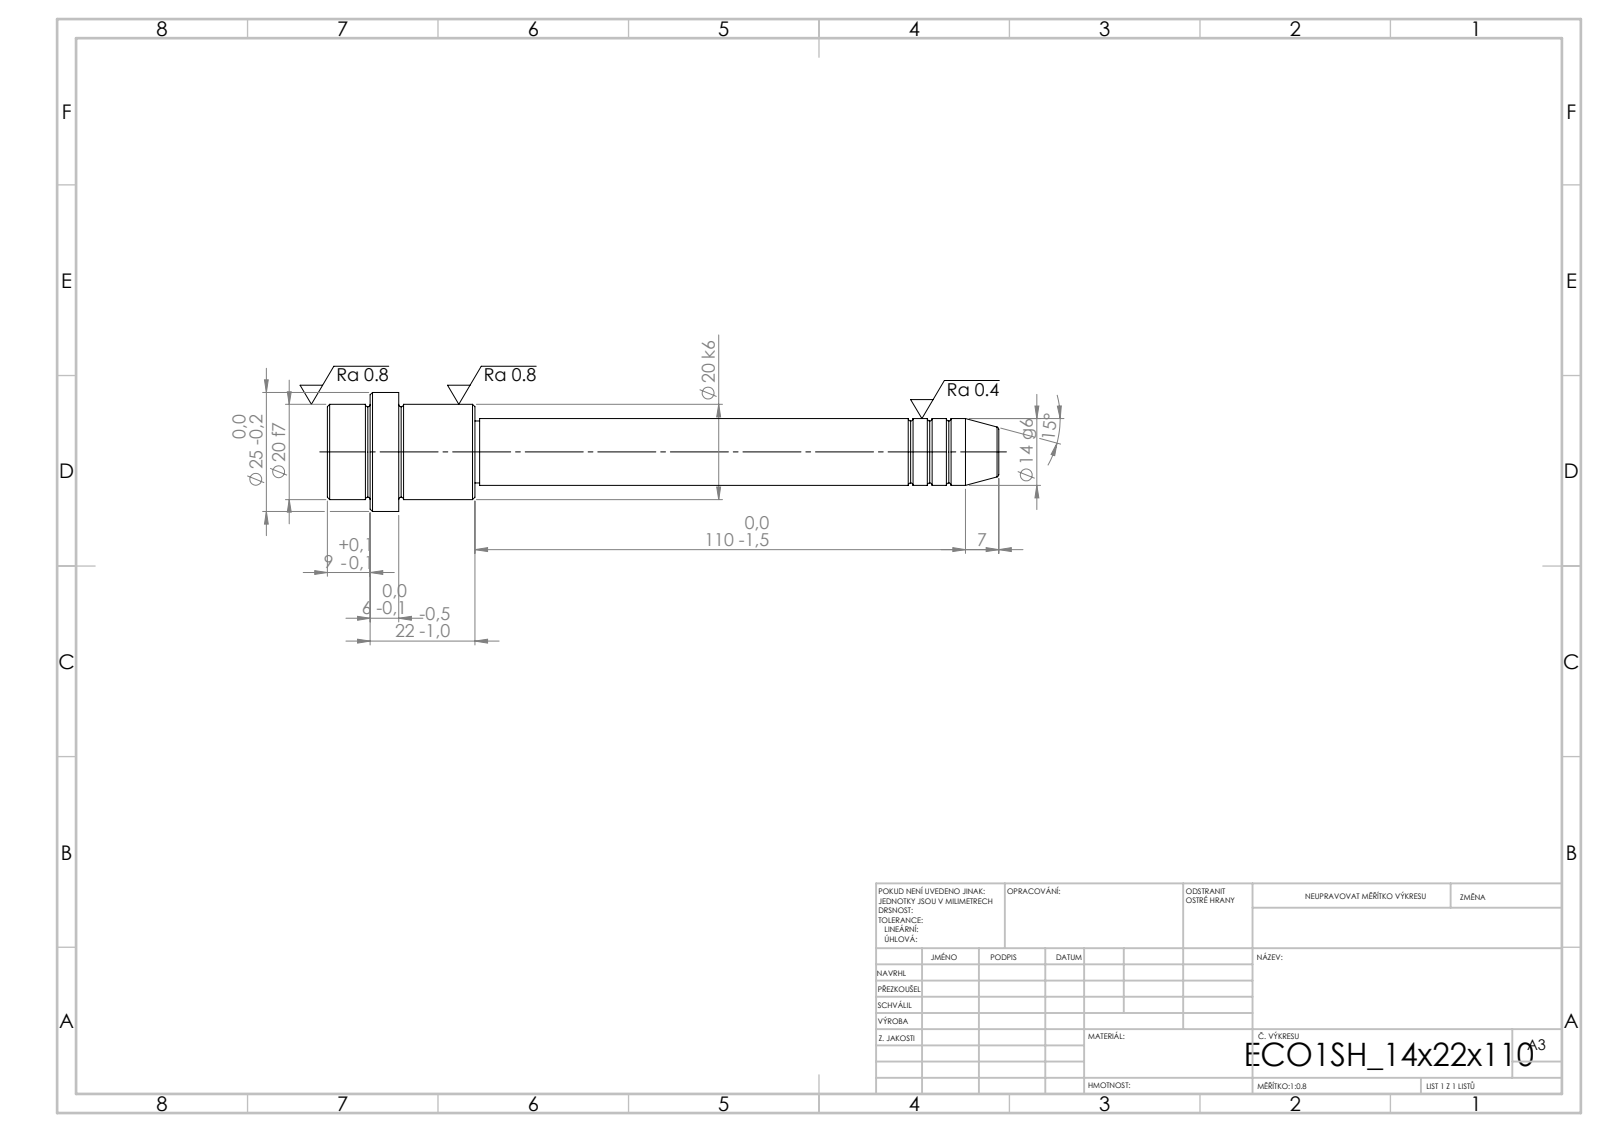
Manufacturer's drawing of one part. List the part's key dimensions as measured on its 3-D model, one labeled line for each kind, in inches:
STEP written by: SolidWorks 2019 (CONFIG_CONTROL_DESIGN)
Units: inches
Bodies: 1 solid, 52 faces (6 planar, 16 cylindrical, 30 other)
Overall size (bounding box): 5.551 × 0.984 × 0.984
Volume: 1.667 in³ · Surface area: 12.19 in²
Round bosses / shafts (diameter × count): ⌀0.984 ×1, ⌀0.787 ×1, ⌀0.551 ×1, ⌀0.512 ×1
Main face-to-face distances: 0.591, 0.63, 1.22, 0.866, 0.236, 0.354, 4.331, 4.961, 5.197, 5.551
